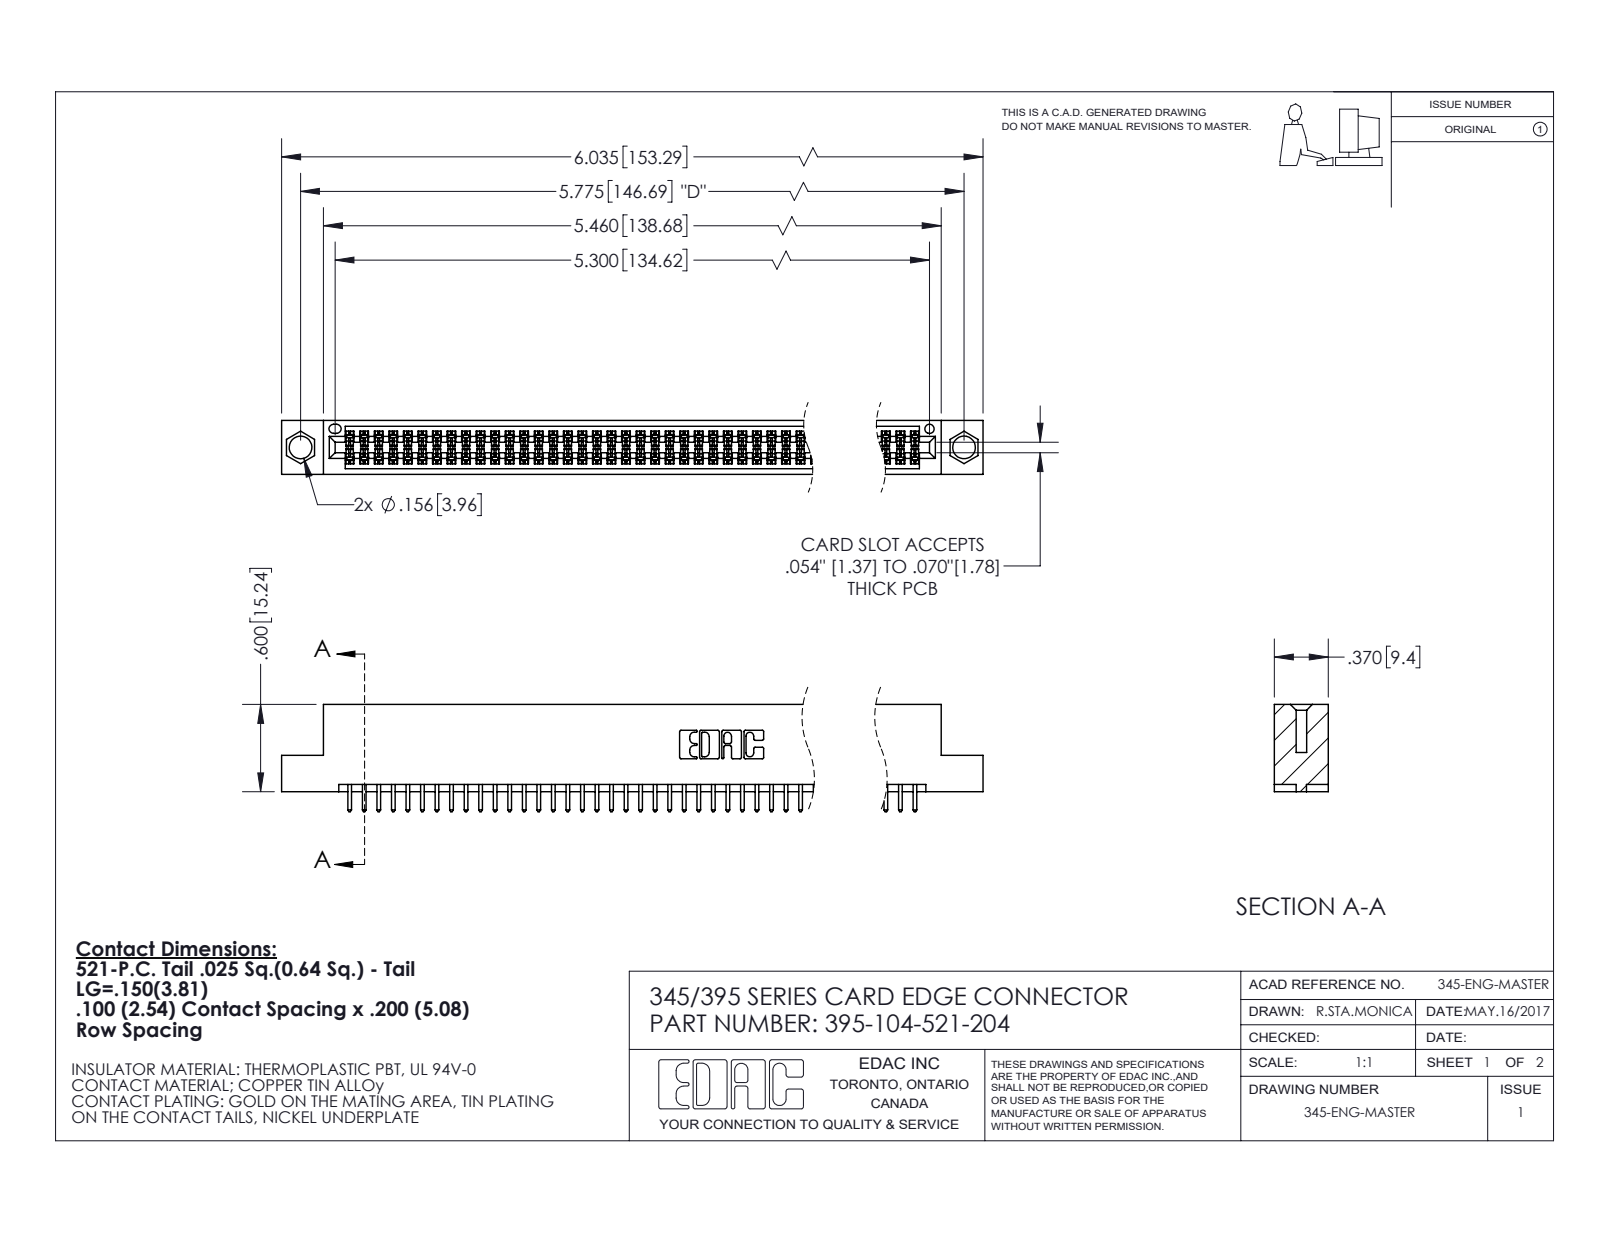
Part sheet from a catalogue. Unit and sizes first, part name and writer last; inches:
Units: inches
Overall size (bounding box): 6.035 × 0.737 × 0.37
Round holes (diameter × count): ⌀0.156 ×2, ⌀0.064 ×1
Partial cylindrical surfaces — rounded edges, fillets, slot ends (radius × count): R0.006 ×156, R0.01 ×104, R0.01 ×22, R0.007 ×6, R0.031 ×6, R0.026 ×3, R0.014 ×2, R0.019 ×2
Main face-to-face distances: 0.298, 0.072, 0.2, 0.37, 0.098, 0.272, 0.025, 0.225, 0.175, 0.149
Hole centre spacings: 0.27, 5.539, 5.775
Volume: 0.905 in³ · Surface area: 33.63 in²
Bodies: 105 solids, 5340 faces (3526 planar, 1814 cylindrical, 0 other)
Part name (STEP PRODUCT): 395-104-521-204; 345 Part_Flush Mounting Lugs - 0.156 Dia-TI; 345-292-001_345-293-121
STEP written by: SolidWorks 2020 (CONFIG_CONTROL_DESIGN)
